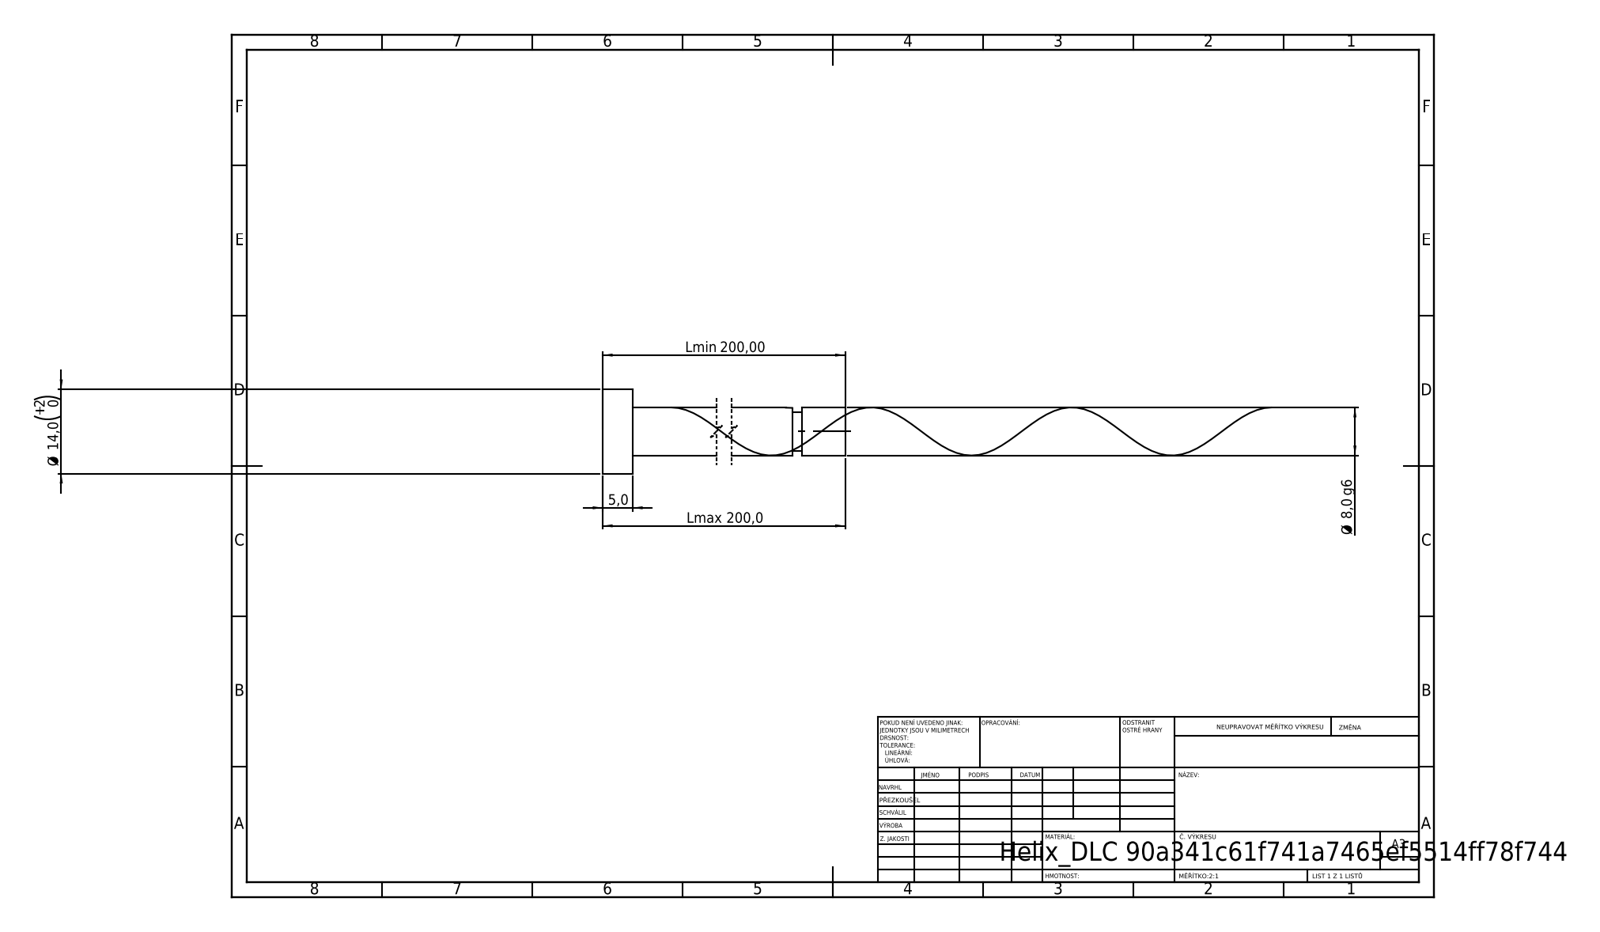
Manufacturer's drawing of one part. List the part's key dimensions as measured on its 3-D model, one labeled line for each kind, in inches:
STEP written by: SolidWorks 2019 (CONFIG_CONTROL_DESIGN)
Units: inches
Bodies: 1 solid, 21 faces (6 planar, 14 cylindrical, 1 other)
Overall size (bounding box): 7.874 × 0.551 × 0.551
Volume: 0.637 in³ · Surface area: 8.618 in²
Round bosses / shafts (diameter × count): ⌀0.551 ×1, ⌀0.315 ×1, ⌀0.252 ×1
Main face-to-face distances: 0.197, 7.874, 7.677, 7.591, 7.394, 0.283, 7.528, 7.331, 0.063, 0.346
